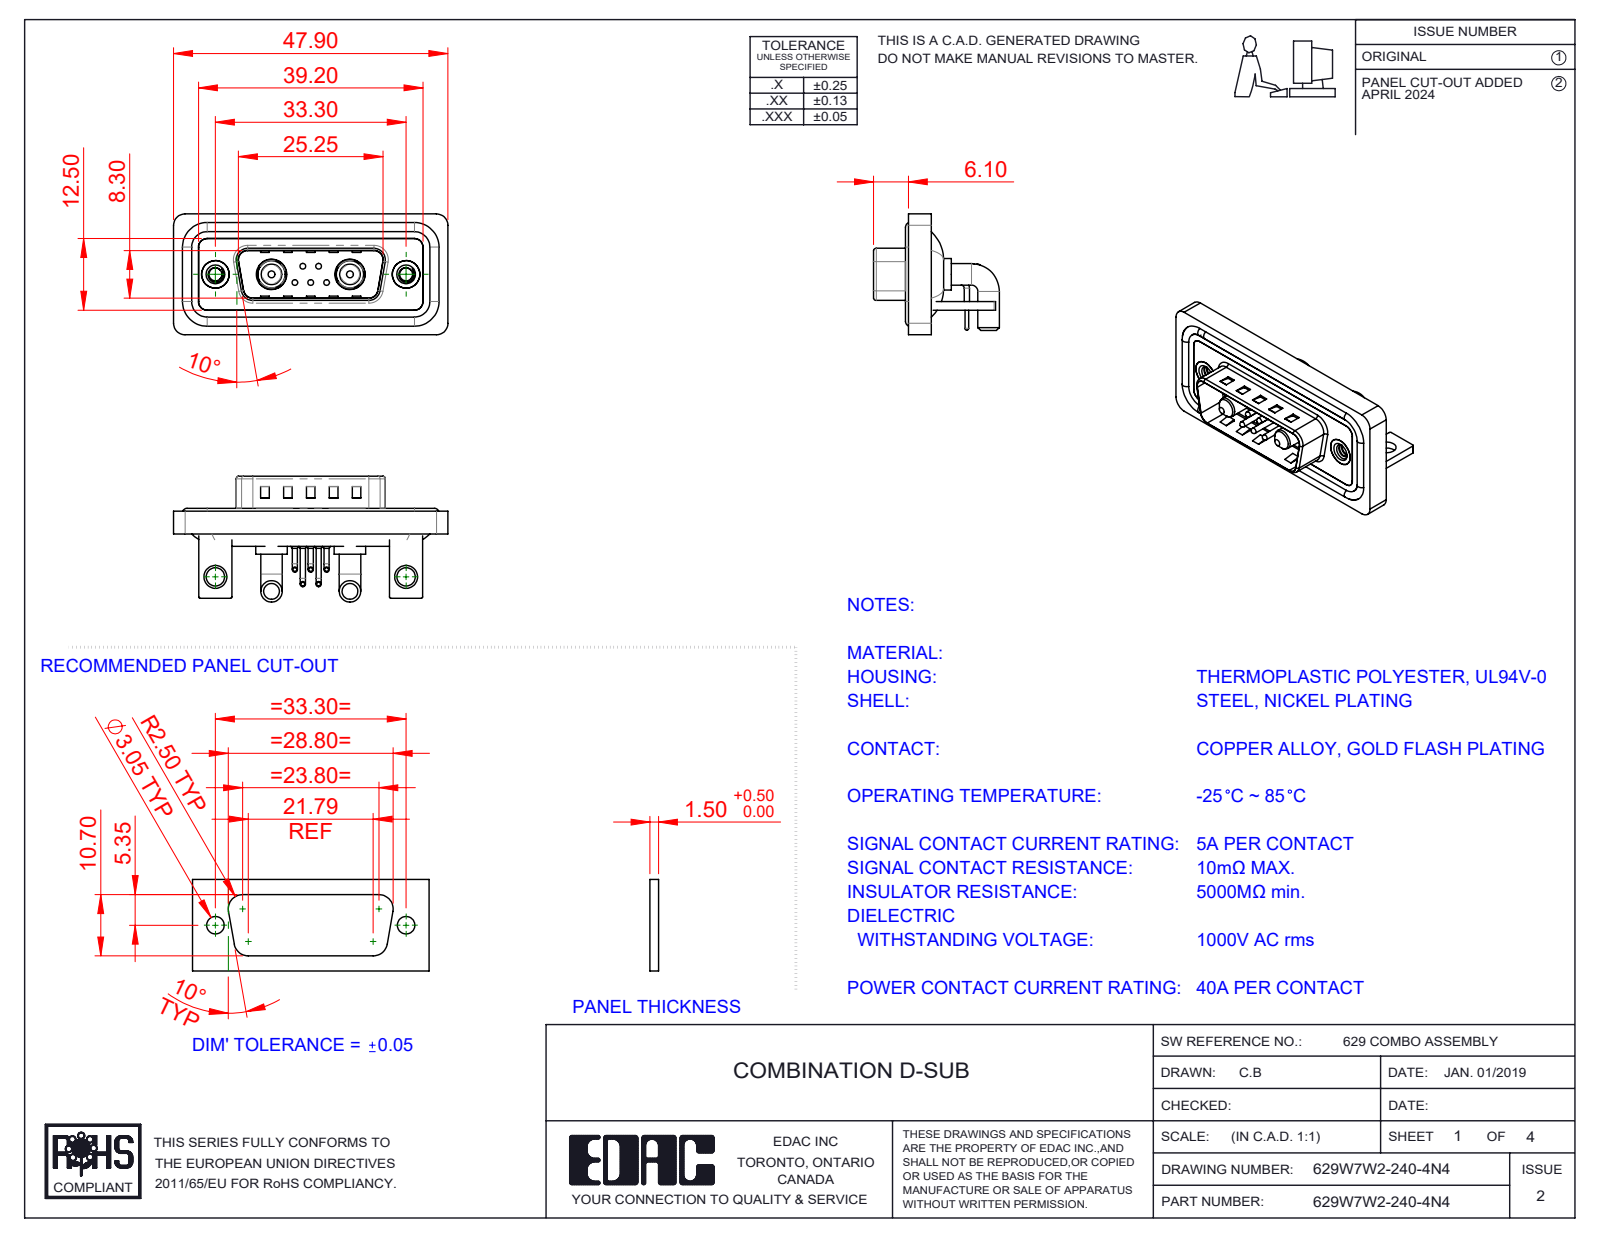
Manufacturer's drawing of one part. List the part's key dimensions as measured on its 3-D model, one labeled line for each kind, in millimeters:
Part name (STEP PRODUCT): Power Pin_40A RA; 629Combo Shell Front_15 Contacts; 629Combo Waterproof Housing_15 Contacts; 629W7W2-140-4N4 (+6 more)
STEP written by: SolidWorks 2023 (CONFIG_CONTROL_DESIGN)
Units: millimetres
Bodies: 18 solids, 1123 faces (537 planar, 424 cylindrical, 162 other)
Overall size (bounding box): 47.9 × 21.98 × 21.1
Volume: 6 104 mm³ · Surface area: 9 815 mm²
Round holes (diameter × count): ⌀0.75 ×5, ⌀1.6 ×5, ⌀2 ×5, ⌀2.26 ×2, ⌀3.2 ×2, ⌀4 ×2, ⌀4.8 ×2, ⌀4.85 ×2, ⌀5 ×2, ⌀5.3 ×2
Round bosses / shafts (diameter × count): ⌀0.9 ×10, ⌀1.5 ×5, ⌀1 ×5, ⌀0.65 ×5, ⌀3.75 ×4, ⌀1.6 ×4, ⌀5.5 ×2, ⌀5.2 ×2
Partial cylindrical surfaces — rounded edges, fillets, slot ends (radius × count): R2 ×21, R1.5 ×18, R0.25 ×16, R0.5 ×9, R1.6 ×8, R1.01 ×5, R0.6 ×4, R0.65 ×4
Main face-to-face distances: 0.4, 1.5, 0.8, 2.9, 2.1, 1.1, 1.6, 1.2, 3.7, 4.5
Hole centre spacings: 3.16, 2.77, 9.8, 23.5, 33.3, 4.31, 4.33, 5.03
